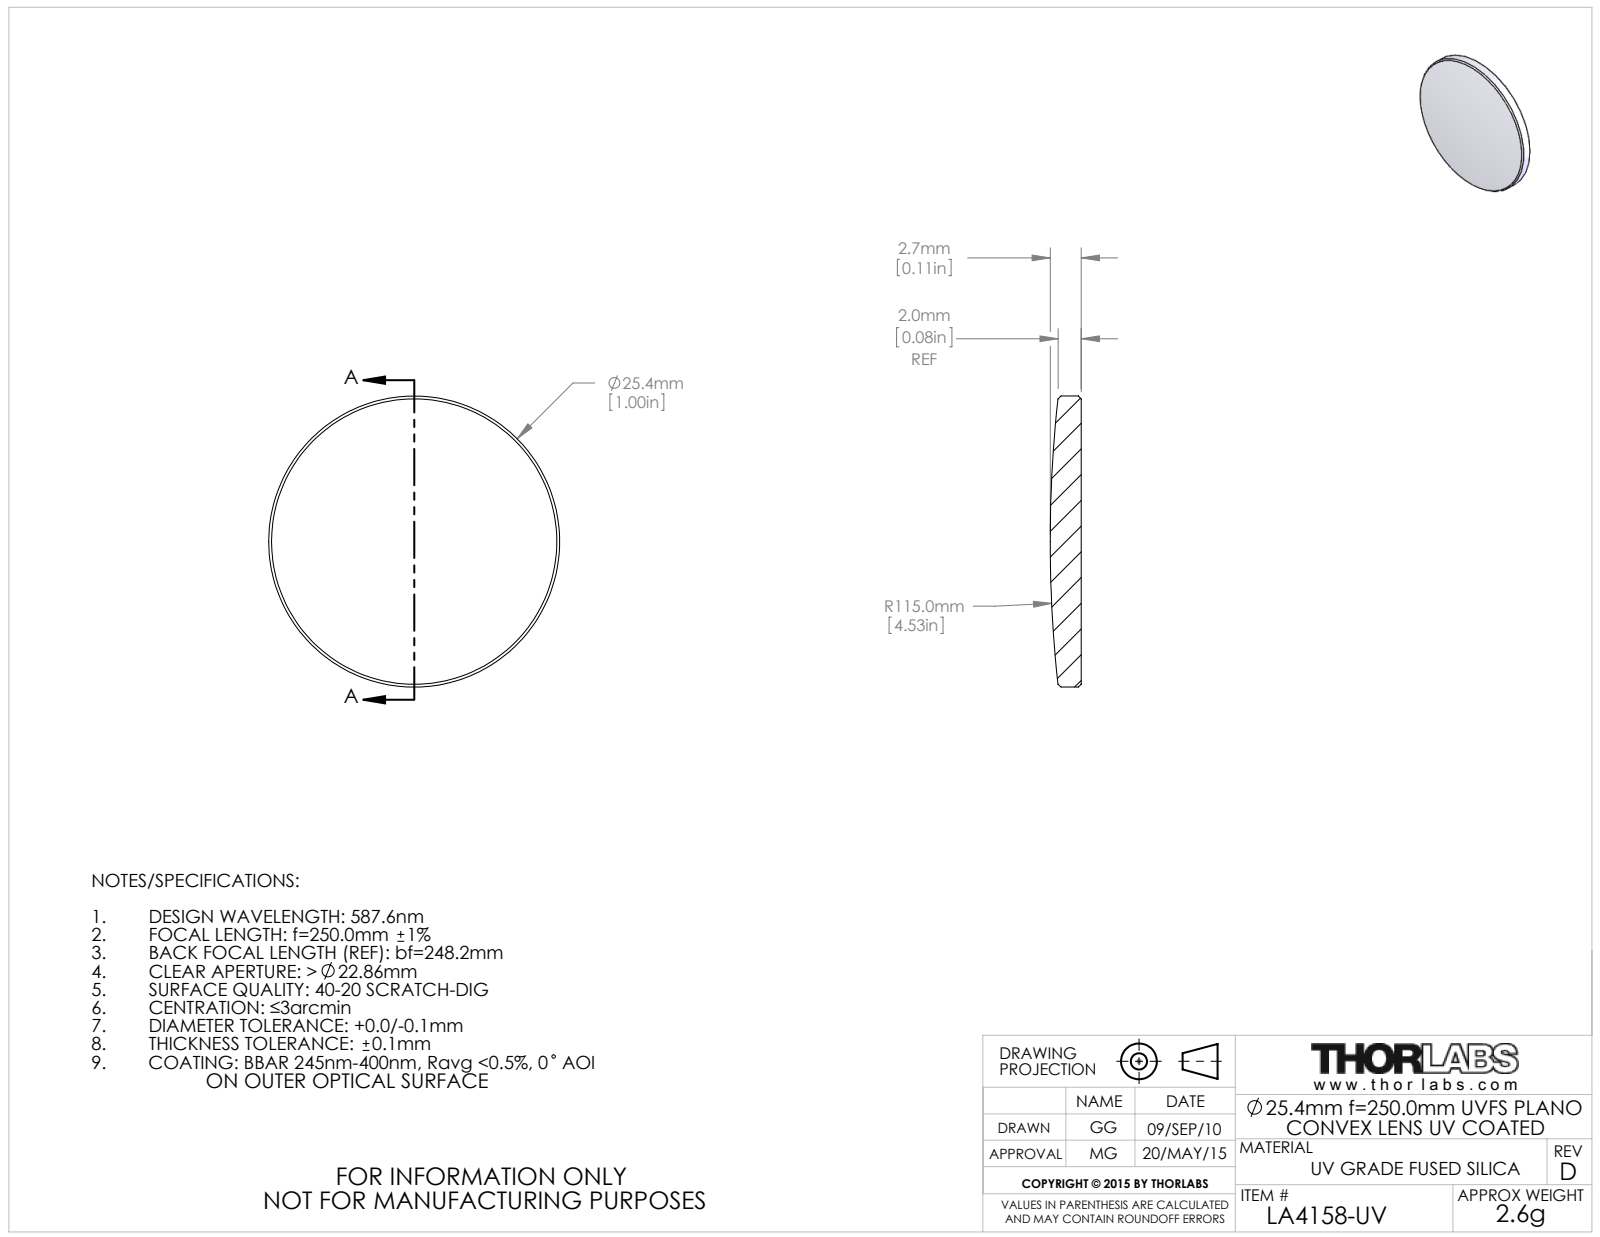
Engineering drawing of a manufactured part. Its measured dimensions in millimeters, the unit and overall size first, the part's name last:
Units: millimetres
Overall size (bounding box): 25.4 × 25.4 × 2.7
Round bosses / shafts (diameter × count): ⌀25.4 ×1
Volume: 1 186 mm³ · Surface area: 1 153 mm²
Bodies: 1 solid, 9 faces (1 planar, 2 cylindrical, 6 other)
Part name (STEP PRODUCT): 4287-E0W
STEP written by: SolidWorks 2014 (CONFIG_CONTROL_DESIGN)
